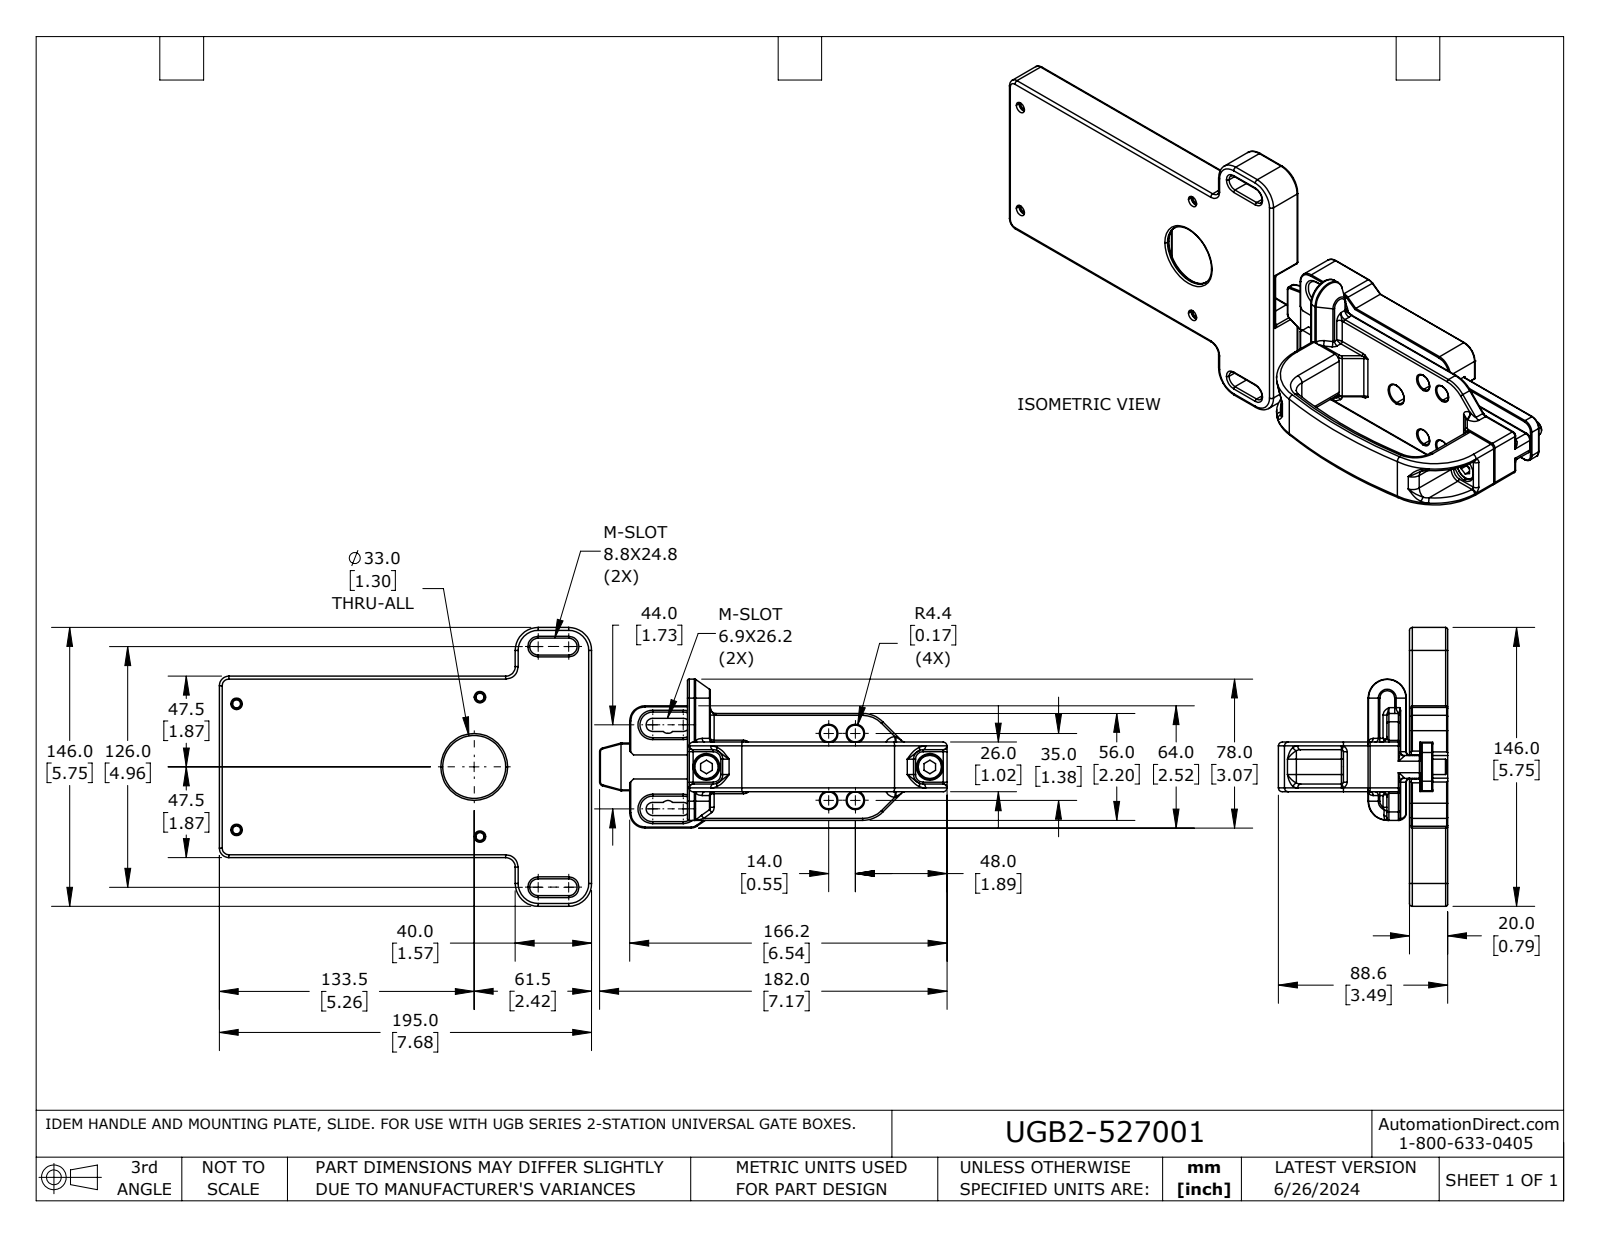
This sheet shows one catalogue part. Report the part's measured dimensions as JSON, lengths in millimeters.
{"part_name": "527001 UGB2-SFH-M", "step_written_by": "SolidWorks 2021 (CONFIG_CONTROL_DESIGN)", "units": "millimeters", "bodies": {"solids": 9, "faces": 1125, "planar": 246, "cylindrical": 505, "other": 374}, "overall_size": [381.19, 146, 88.6], "volume_mm3": 338592, "surface_area_mm2": 152913, "round_holes": [[4.2, 6], [8.8, 6], [5, 4], [6, 4], [6.75, 2], [14, 2], [9, 1], [11, 1], [33, 1]], "round_bosses_or_shafts": [[13, 2], [9, 2], [8, 2], [5, 2]], "partial_cylinders_radius": [[1, 98], [0.5, 60], [2, 50], [3, 22], [5, 20], [1.5, 7], [3.45, 6], [4.4, 4]], "face_to_face_distances": [2.5, 17.5, 20, 7, 12.2, 19, 6.2, 7.8, 9.7, 13.8], "hole_center_spacings": [10.3, 122.33, 14, 18, 26.58, 35, 36.62, 37.7]}
